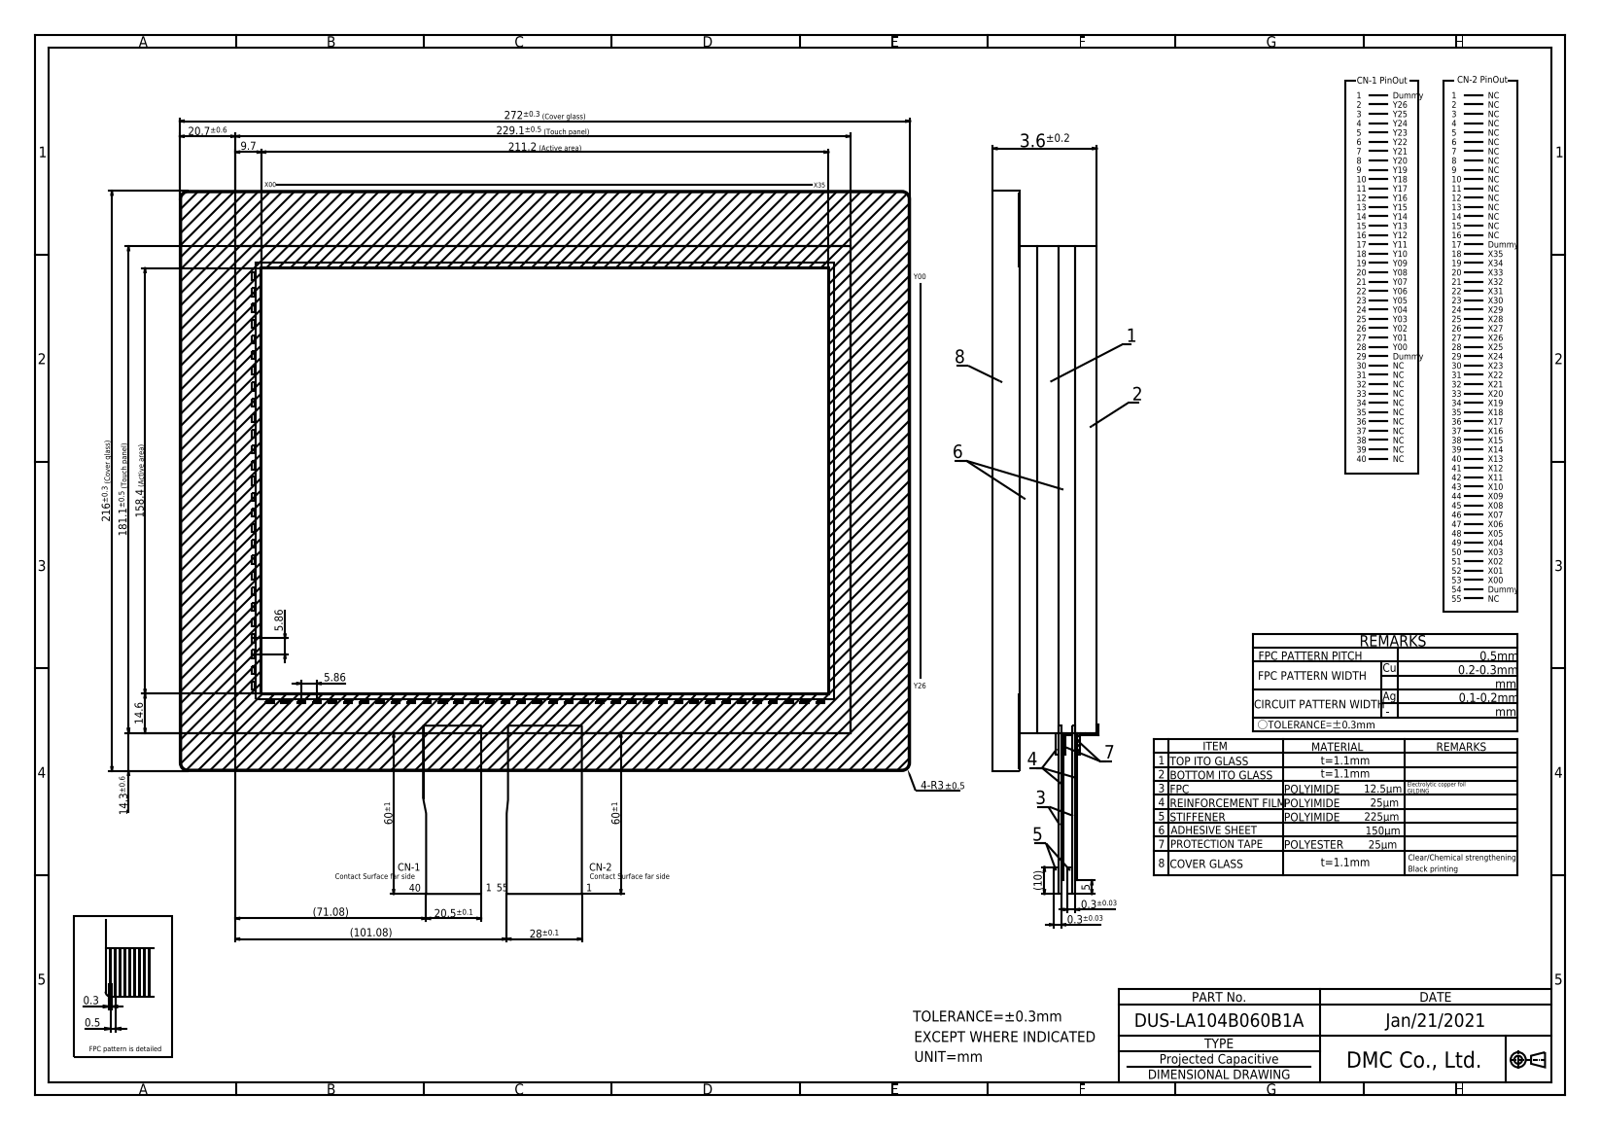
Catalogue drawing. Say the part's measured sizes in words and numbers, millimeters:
The part is named "DUS-LA104B060B1A". Its 3-D file was written by "Autodesk Inventor 2020 (CONFIG_CONTROL_DESIGN)". It is 1 solid with 425 faces: 420 planar, 5 cylindrical and 0 other. Overall it measures 380.8 by 304.9 by 3.6 millimeters. Its volume is 165 411 cubic millimeters and its surface area 193 509 square millimeters. Partial cylindrical surfaces (rounded edges, fillets, slot ends): 4 of radius 3, 1 of radius 0.2. The main face-to-face distances are 1.1, 2.5, 3.6, 1.2, 2.4, 1.25, 1.15, 1.35, 2.45, 2.35.
